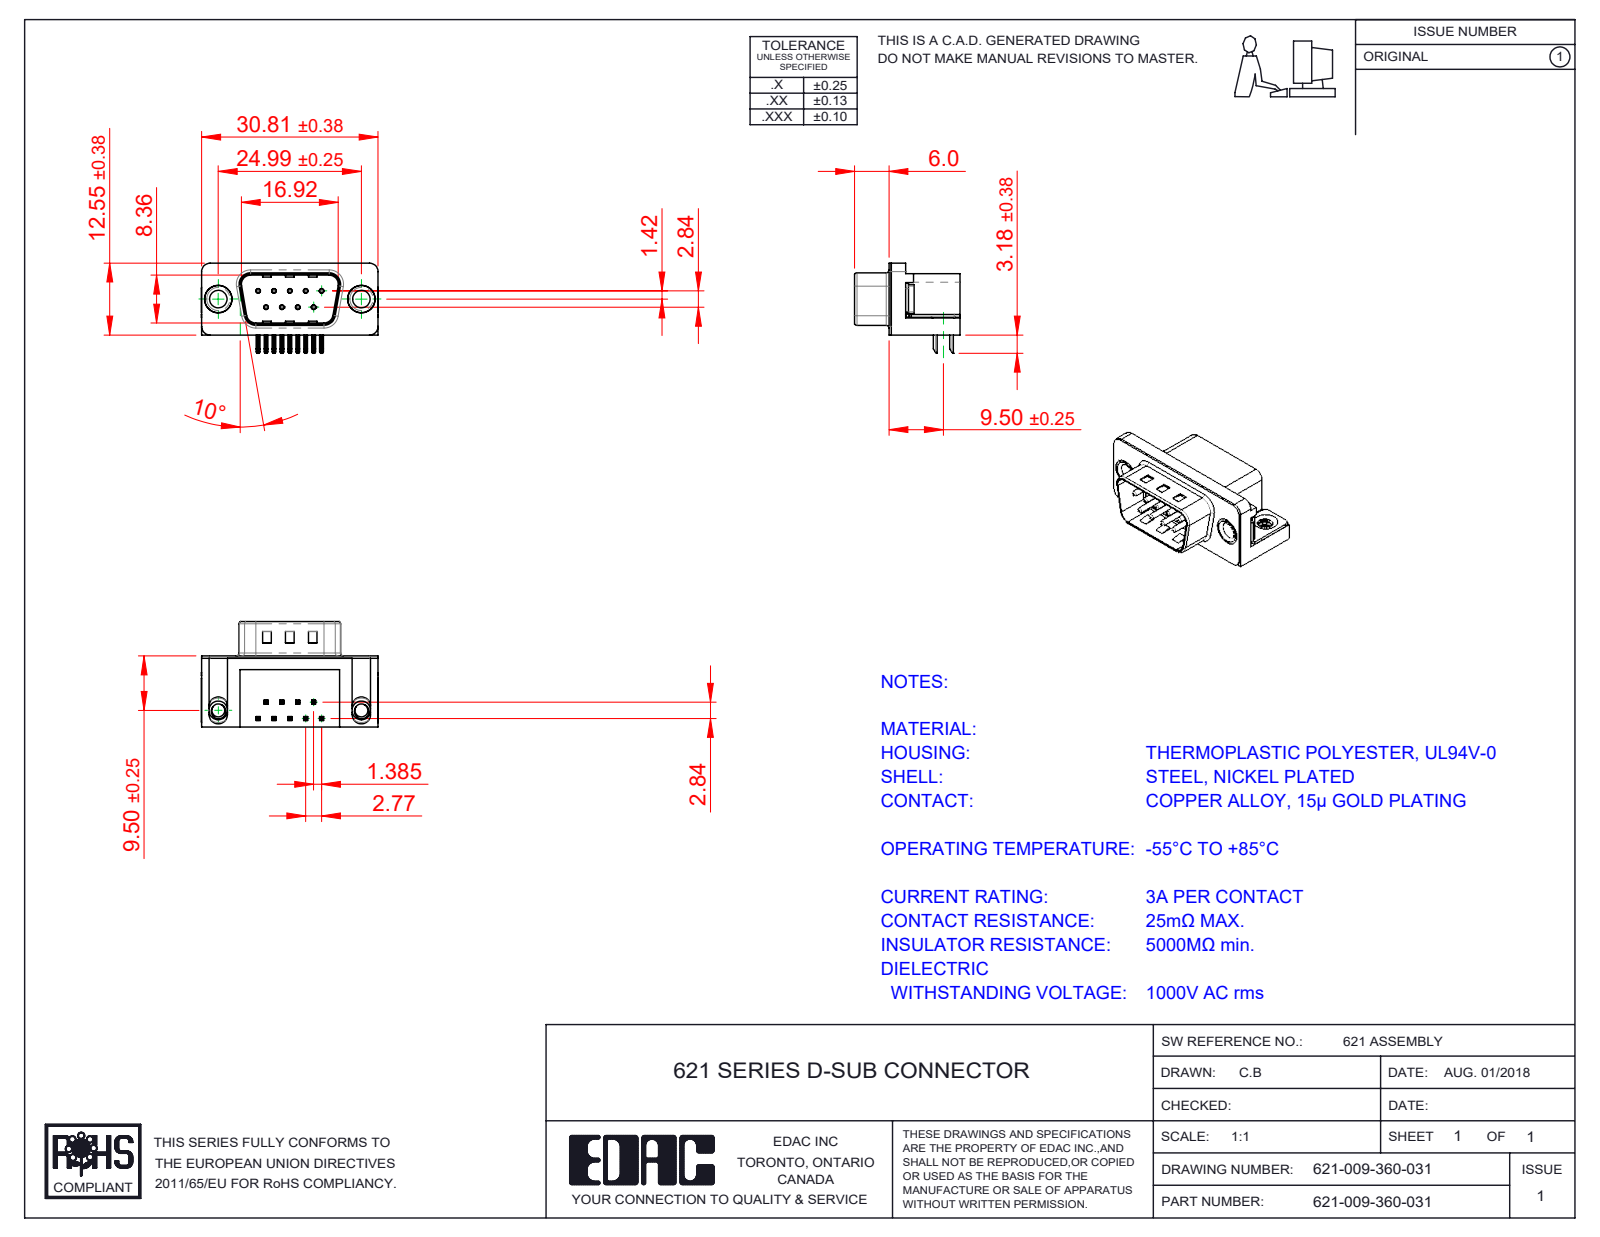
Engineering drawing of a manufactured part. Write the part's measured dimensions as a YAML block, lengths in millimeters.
part_name: "621 Thru Hole Rivet; 621 2 Prong Board Lock; 621 Contact Bottom; 621 Contact Top (+3 more)"
step_written_by: "SolidWorks 2016 (CONFIG_CONTROL_DESIGN)"
units: millimeters
bodies: {solids: 15, faces: 991, planar: 605, cylindrical: 305, other: 81}
overall_size: [30.89, 18.4, 16.25]
volume: 3233
surface_area: 4403
round_holes:
  - {diameter: 0.35, count: 9}
  - {diameter: 0.8, count: 9}
  - {diameter: 3.05, count: 2}
  - {diameter: 4, count: 2}
  - {diameter: 4.8, count: 2}
  - {diameter: 5, count: 2}
round_bosses_or_shafts:
  - {diameter: 0.75, count: 9}
  - {diameter: 4.9, count: 2}
  - {diameter: 4.75, count: 2}
  - {diameter: 3.85, count: 2}
partial_cylinders:
  - {radius: 0.25, count: 44}
  - {radius: 0.12, count: 18}
  - {radius: 1, count: 16}
  - {radius: 0.5, count: 14}
  - {radius: 1.5, count: 8}
  - {radius: 1.6, count: 8}
  - {radius: 0.32, count: 4}
  - {radius: 0.9, count: 4}
face_to_face_distances: [0.4, 12, 12.4, 10.35, 0.5, 9.5, 2.5, 2.9, 2.1, 0.35]
hole_center_spacings: [3.16, 2.77, 5.54, 5.03, 5.04, 8.31, 7.48, 7.49]
